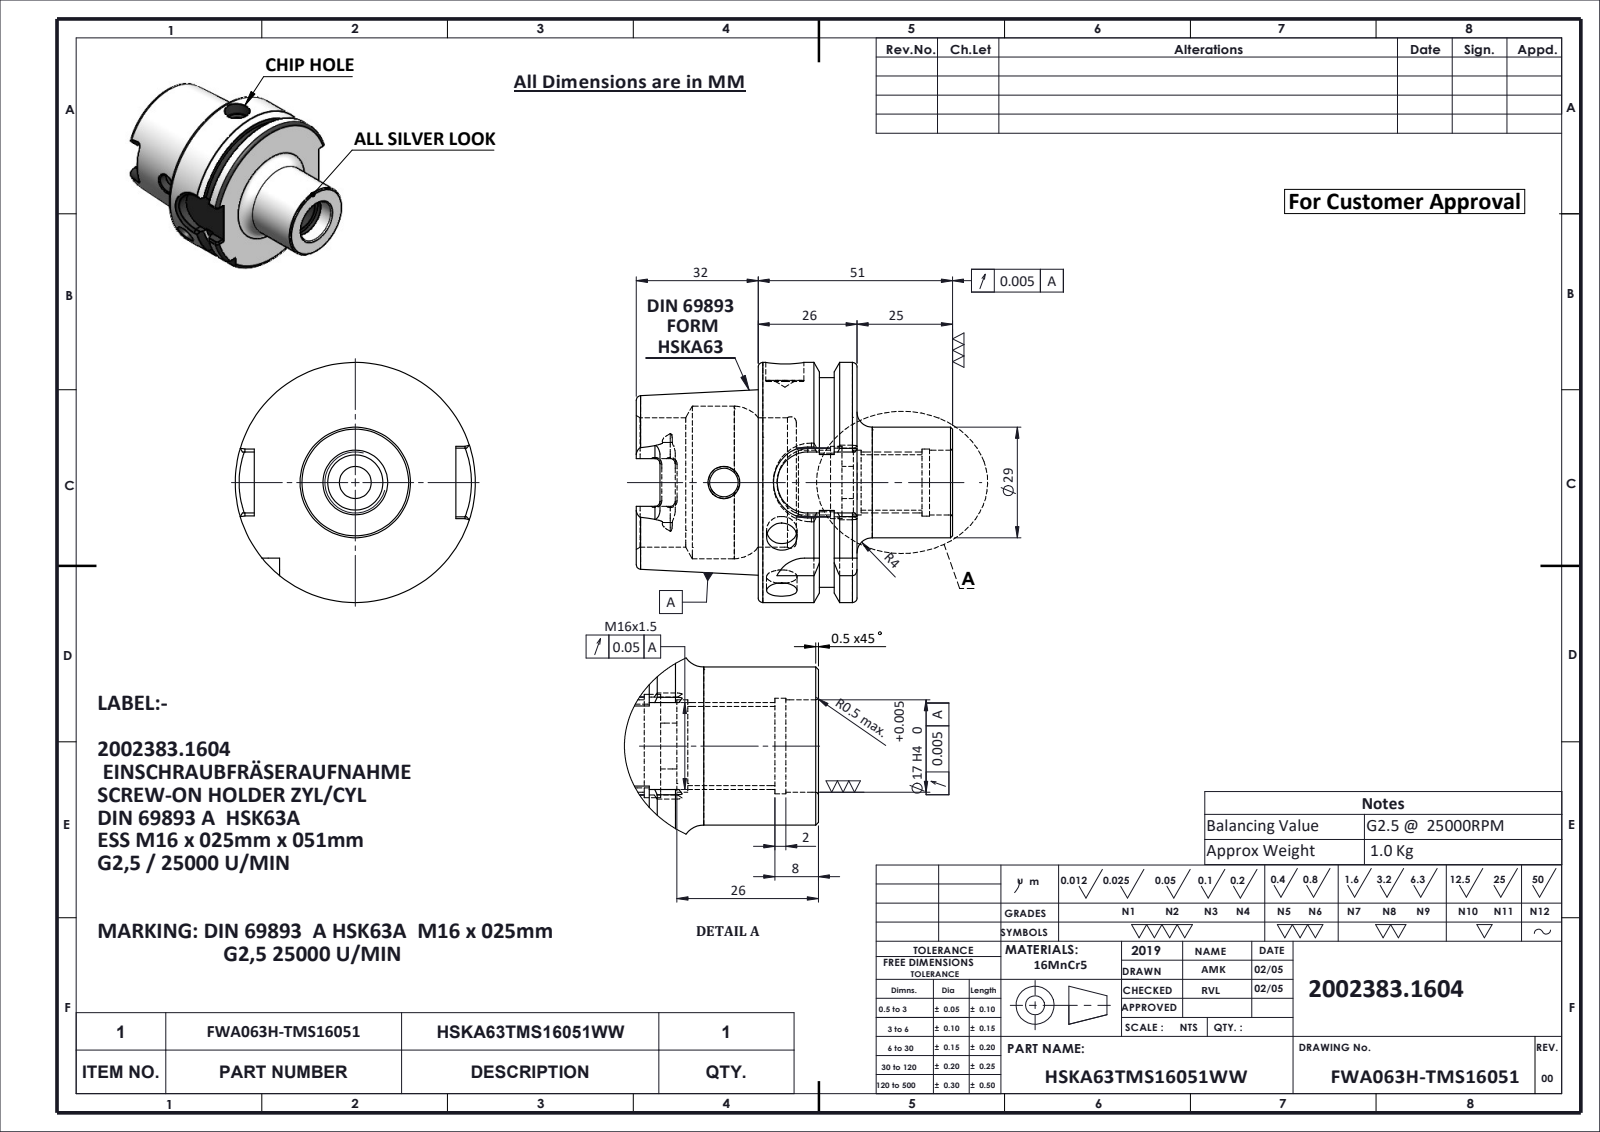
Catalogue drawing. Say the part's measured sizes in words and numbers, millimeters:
The part is named "FWA063H-TMS16051; HSKA63TMS16051WW". Its 3-D file was written by "SolidWorks 2024 (CONFIG_CONTROL_DESIGN)". It is 1 solid with 170 faces: 53 planar, 55 cylindrical and 62 other. Overall it measures 83 by 63 by 63 millimeters. Its volume is 92 783 cubic millimeters and its surface area 25 831 square millimeters. Round holes: 2 of diameter 8, 1 of diameter 7.5, 1 of diameter 8.4, 1 of diameter 10, 1 of diameter 14.5, 1 of diameter 17, 1 of diameter 17.6, 1 of diameter 19, 1 of diameter 34, 1 of diameter 40. Round bosses or shafts: 1 of diameter 63, 1 of diameter 55, 1 of diameter 29. Partial cylindrical surfaces (rounded edges, fillets, slot ends): 6 of radius 1.3, 4 of radius 2.88, 2 of radius 8, 1 of radius 9. The main face-to-face distances are 25.95, 10, 15.95, 32, 51, 42, 57.95, 83, 41, 25.05.
